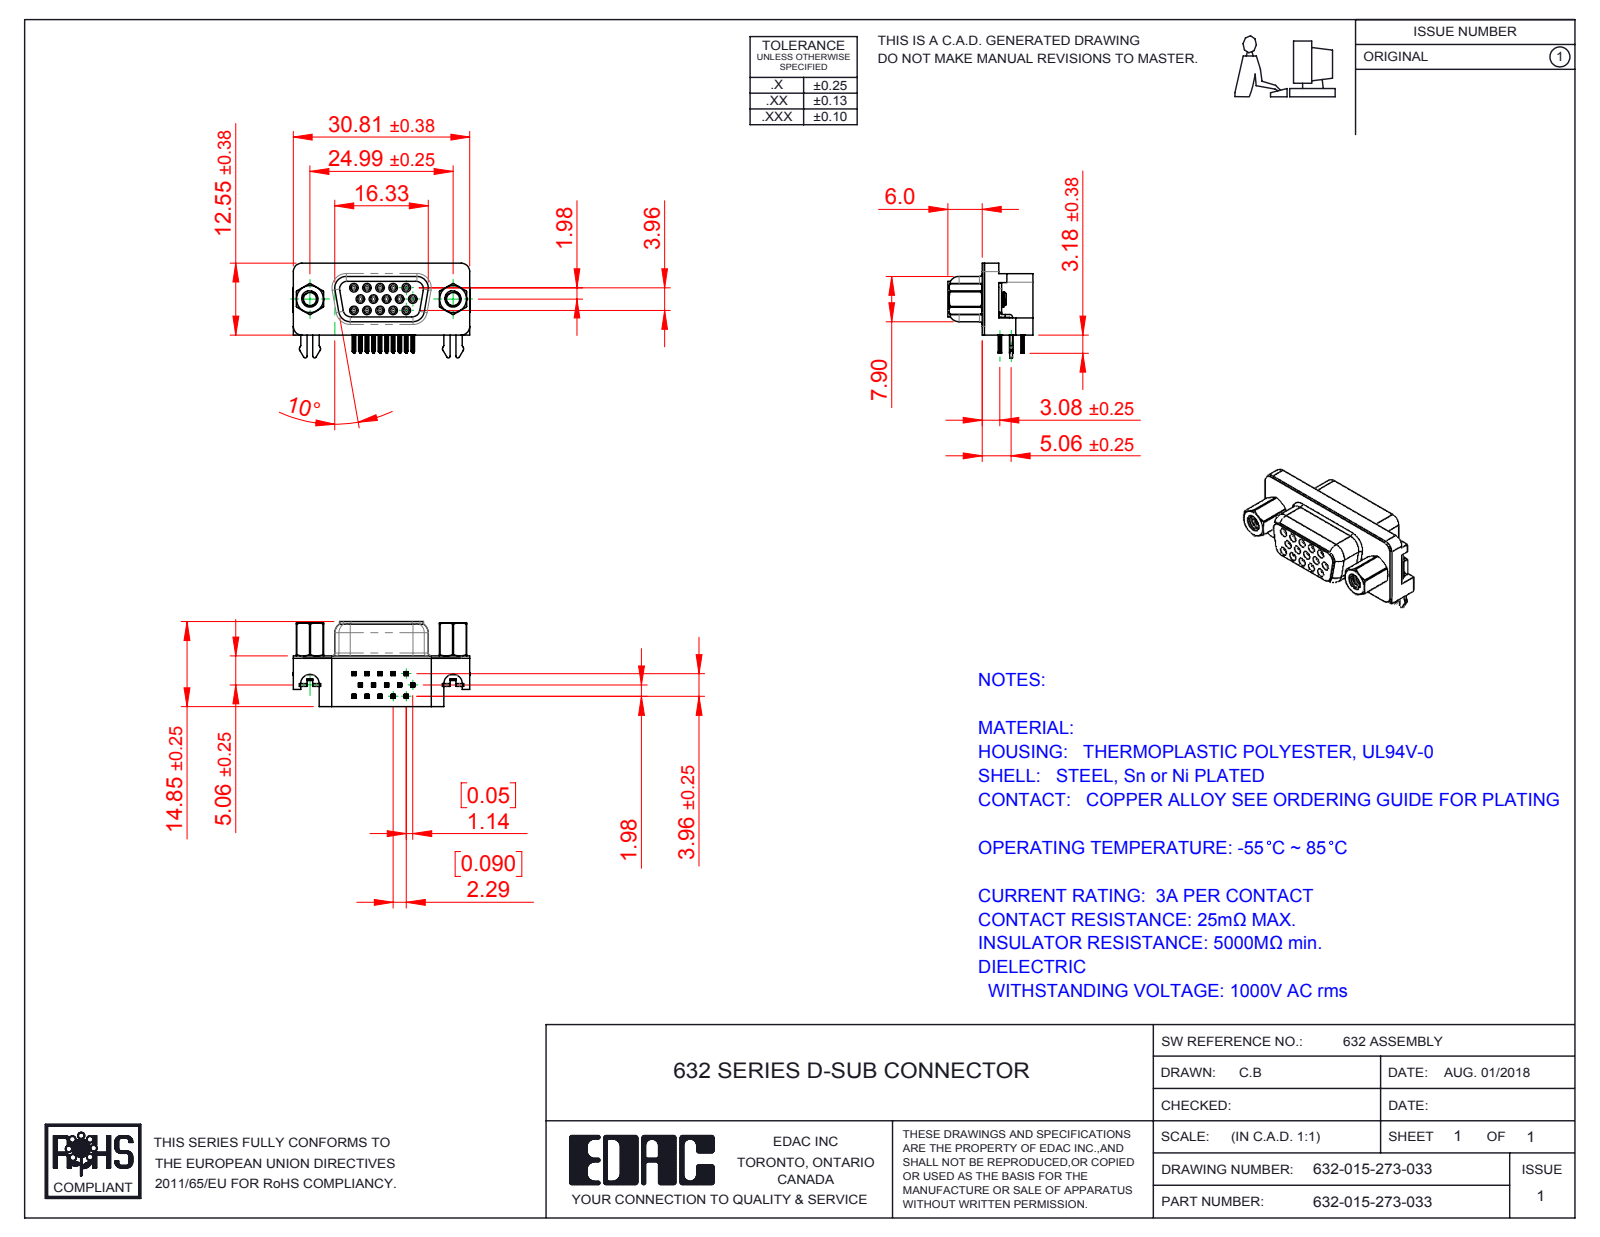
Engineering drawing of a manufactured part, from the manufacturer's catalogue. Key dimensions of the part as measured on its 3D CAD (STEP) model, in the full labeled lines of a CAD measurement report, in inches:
Part name (STEP PRODUCT): 632 Contact Middle_Recessed; 632 Contact Top; 632 4-40 Hex Standoff 5; 632 Contact Middle (+5 more)
STEP written by: SolidWorks 2016 (CONFIG_CONTROL_DESIGN)
Units: inches
Bodies: 21 solids, 2376 faces (996 planar, 646 cylindrical, 734 other)
Overall size (bounding box): 1.216 × 0.652 × 0.585
Volume: 0.186 in³ · Surface area: 8.024 in²
Round holes (diameter × count): ⌀0.031 ×15, ⌀0.035 ×15, ⌀0.09 ×2, ⌀0.157 ×2, ⌀0.189 ×2, ⌀0.197 ×2
Round bosses / shafts (diameter × count): ⌀0.047 ×15, ⌀0.193 ×2, ⌀0.11 ×2
Partial cylindrical surfaces — rounded edges, fillets, slot ends (radius × count): R0.004 ×120, R0.006 ×60, R0.014 ×30, R0.013 ×15, R0.039 ×11, R0.011 ×10, R0.02 ×10, R0.053 ×8
Main face-to-face distances: 0.016, 0.078, 0.333, 0.348, 0.114, 0.098, 0.234, 0.264, 0.278, 0.125
Hole centre spacings: 0.09, 0.09, 0.156, 0.18, 0.238, 0.156, 0.18, 0.27
